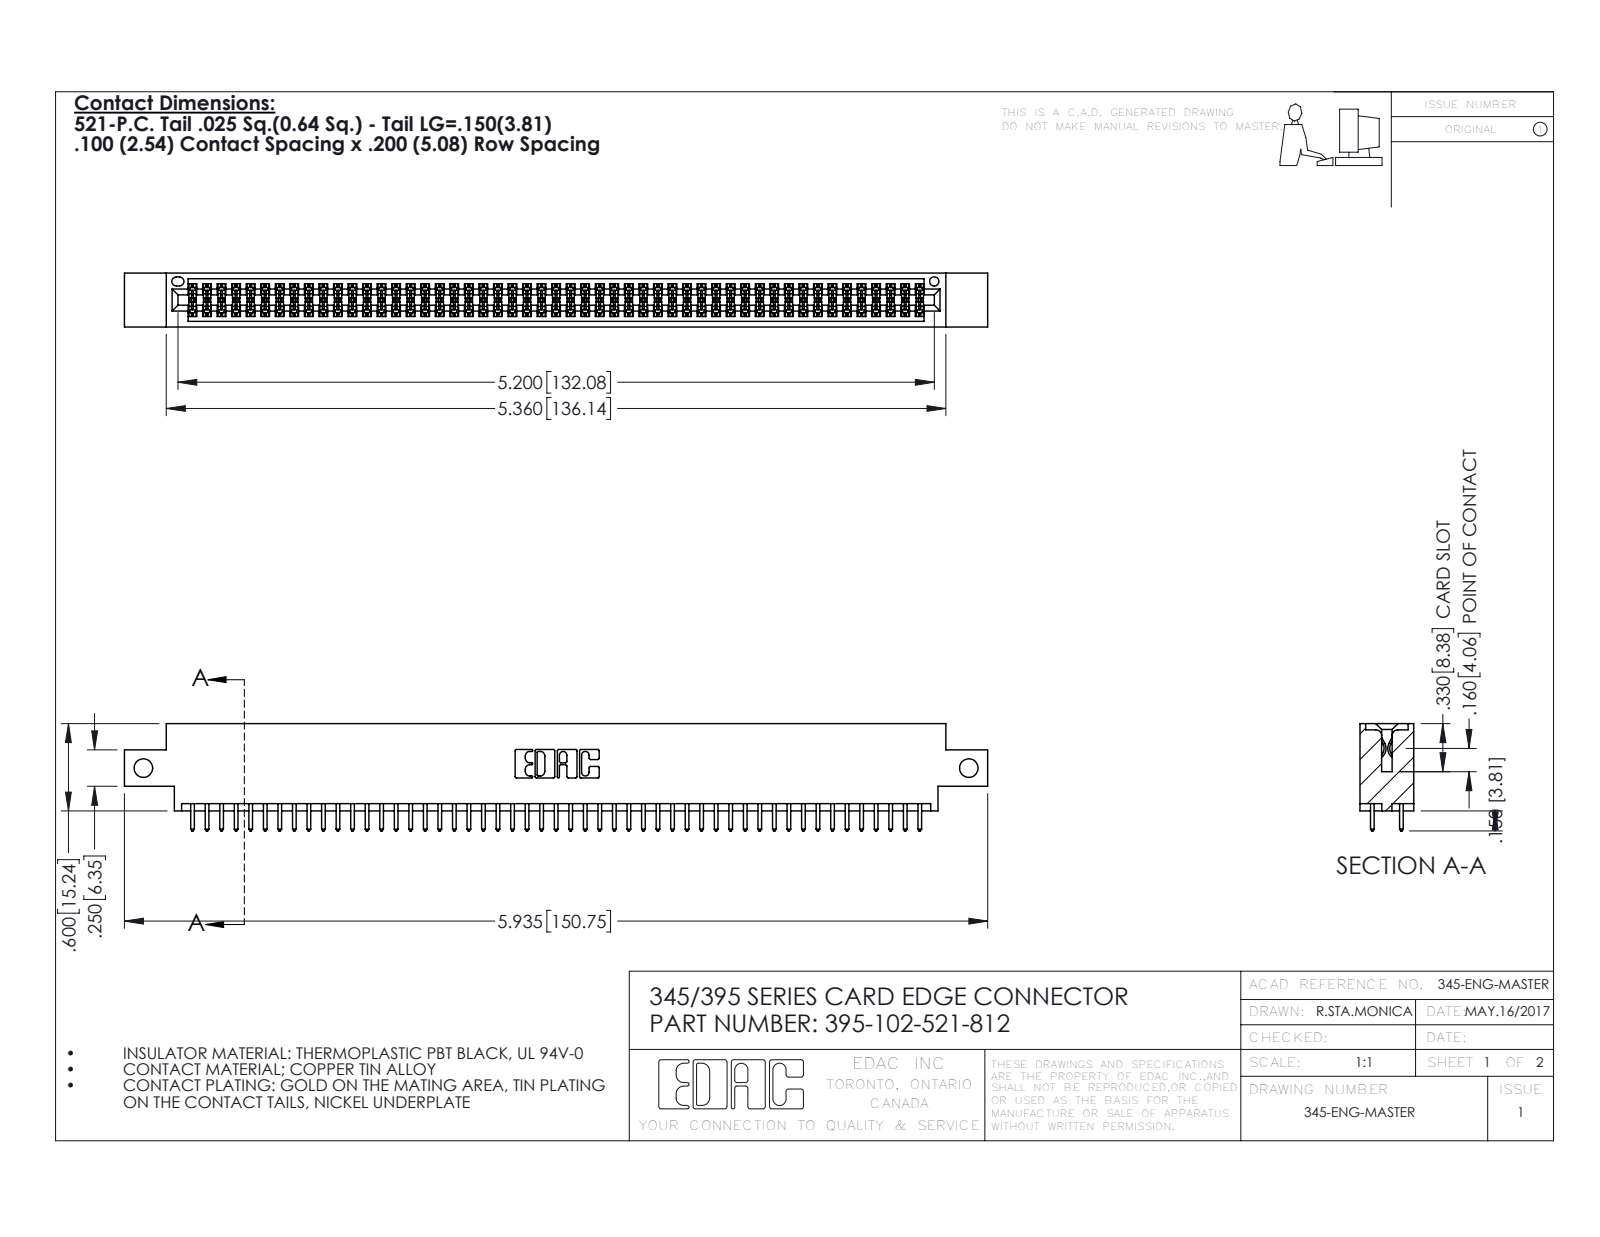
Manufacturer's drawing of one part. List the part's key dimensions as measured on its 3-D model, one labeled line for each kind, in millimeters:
Part name (STEP PRODUCT): 345-292-001_345-293-121; 395-102-521-812; 345 Part_0.170 Offset - Side Mount
STEP written by: SolidWorks 2016 (CONFIG_CONTROL_DESIGN)
Units: millimetres
Bodies: 103 solids, 5230 faces (3450 planar, 1780 cylindrical, 0 other)
Overall size (bounding box): 150.7 × 18.7 × 9.4
Volume: 14 500 mm³ · Surface area: 21 320 mm²
Round holes (diameter × count): ⌀3.3 ×2, ⌀1.6 ×1
Partial cylindrical surfaces — rounded edges, fillets, slot ends (radius × count): R0.2 ×153, R0.3 ×102, R0.3 ×22, R0.2 ×6, R0.8 ×6, R0.7 ×3, R0.4 ×2, R0.5 ×2
Main face-to-face distances: 7.6, 1.8, 5.1, 9.4, 2.5, 6.9, 0.6, 5.7, 4.4, 3.8
Hole centre spacings: 144.1
